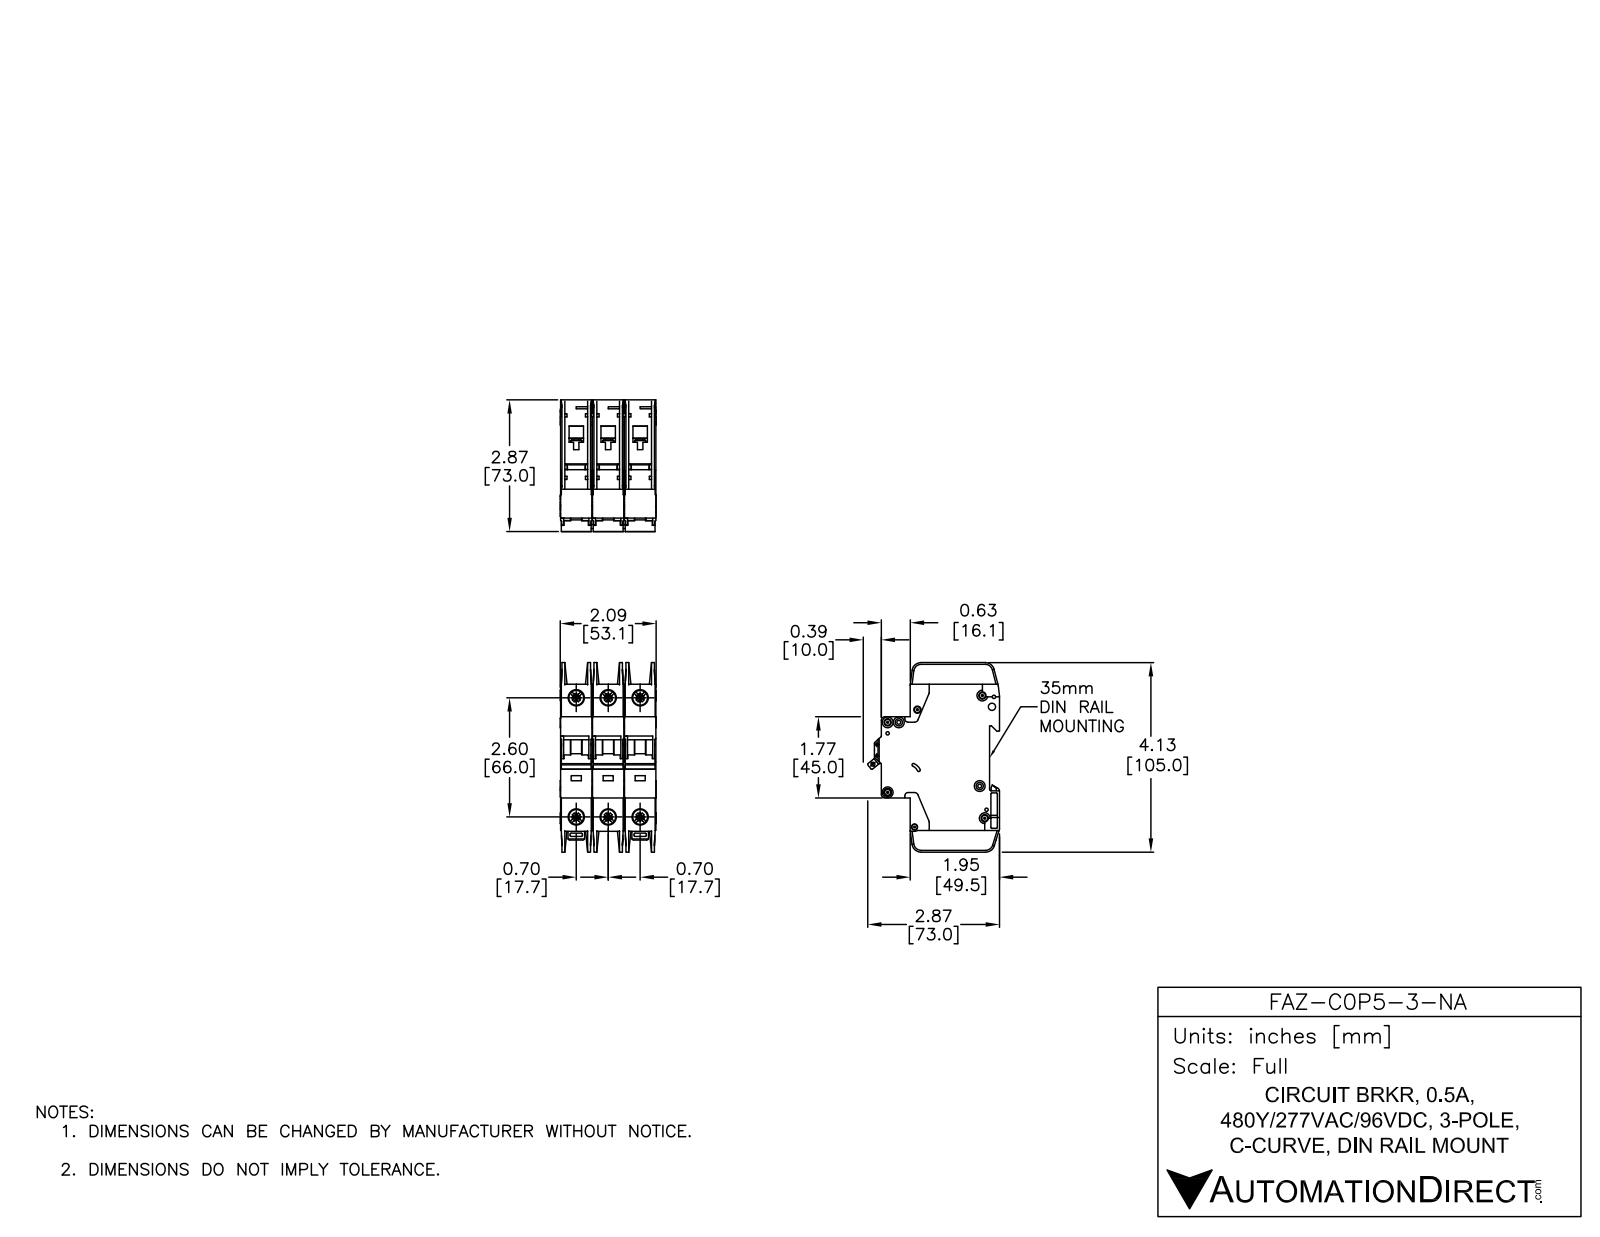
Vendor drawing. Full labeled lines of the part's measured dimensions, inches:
Part name (STEP PRODUCT): FAZ-C0P5-3-NA
STEP written by: SolidWorks 2014 (AUTOMOTIVE_DESIGN)
Units: inches
Bodies: 9 solids, 2352 faces (1227 planar, 789 cylindrical, 336 other)
Overall size (bounding box): 4.134 × 2.876 × 2.091
Volume: 14.22 in³ · Surface area: 115 in²
Round holes (diameter × count): ⌀0.142 ×7, ⌀0.281 ×6, ⌀0.323 ×6, ⌀0.043 ×2, ⌀0.059 ×2, ⌀0.157 ×2, ⌀0.075 ×1, ⌀0.085 ×1, ⌀0.087 ×1, ⌀0.1 ×1, ⌀0.13 ×1, ⌀0.134 ×1
Round bosses / shafts (diameter × count): ⌀0.236 ×7, ⌀0.098 ×3
Partial cylindrical surfaces — rounded edges, fillets, slot ends (radius × count): R0.01 ×65, R0.02 ×30, R0.039 ×26, R0.079 ×14, R0.071 ×5, R0.197 ×5, R0.157 ×4, R0.008 ×2
Main face-to-face distances: 0.697, 1.394, 0.689, 1.386, 0.028, 0.593, 0.096, 0.069, 0.62, 0.524
Hole centre spacings: 0.697, 2.69, 2.598, 0.244, 1.394, 2.948, 0.204, 0.24
